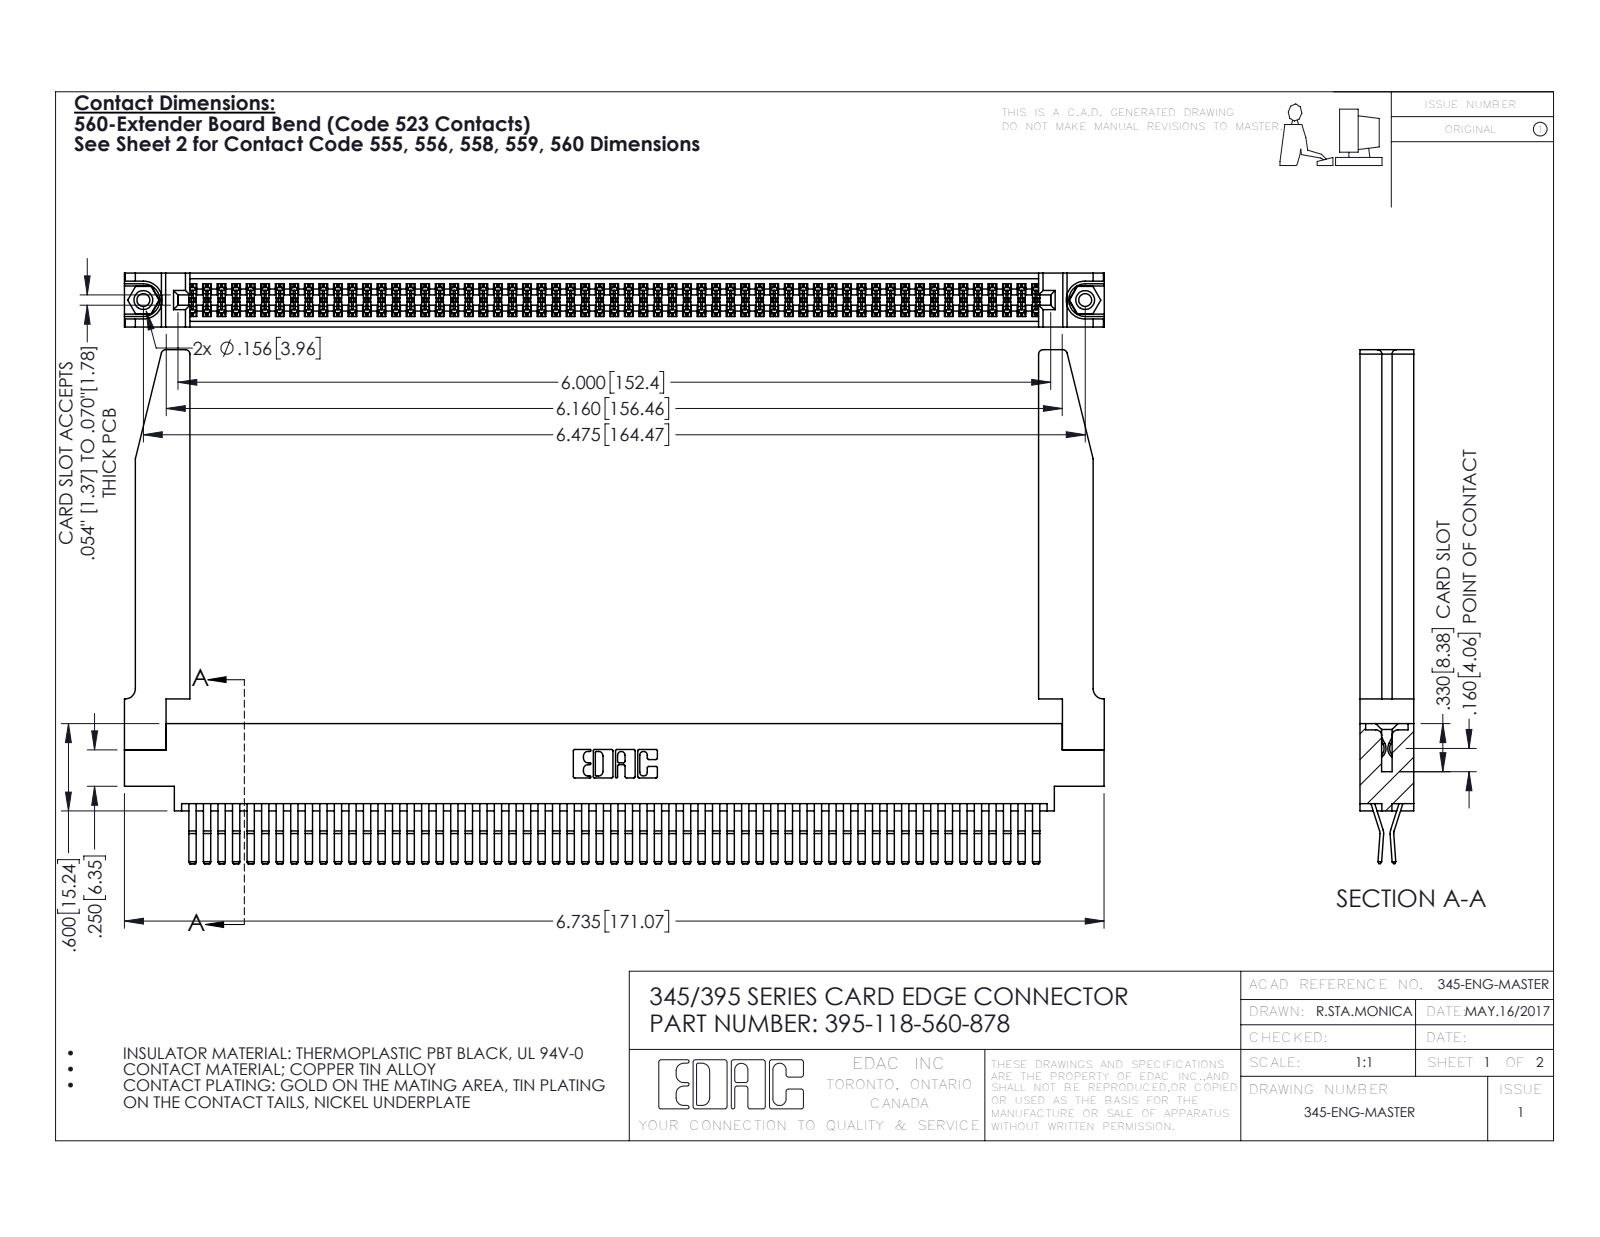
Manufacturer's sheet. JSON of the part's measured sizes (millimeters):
{"part_name": "345 Part_0.170 Offset - 0.156 Dia-TH; 345-250-001_345-250-001-102; 345-220-078_345-220-078; 345-292-001_560 Tail (+1 more)", "step_written_by": "SolidWorks 2016 (CONFIG_CONTROL_DESIGN)", "units": "millimeters", "bodies": {"solids": 123, "faces": 6500, "planar": 4120, "cylindrical": 2328, "other": 52}, "overall_size": [171.1, 89.7, 9.4], "volume_mm3": 25200, "surface_area_mm2": 35080, "round_holes": [[2.3, 2], [3.2, 2], [4, 2], [1.6, 1]], "round_bosses_or_shafts": [[3.9, 2]], "partial_cylinders_radius": [[0.2, 177], [0.3, 22], [0.8, 8], [0.2, 6], [0.8, 6], [0.7, 3], [0.3, 2], [0.4, 2]], "face_to_face_distances": [1.8, 9.4, 7.6, 0.6, 2.5, 6.9, 5.1, 5.7, 4.4, 3.8], "hole_center_spacings": [6.9, 158.5, 164.5]}
